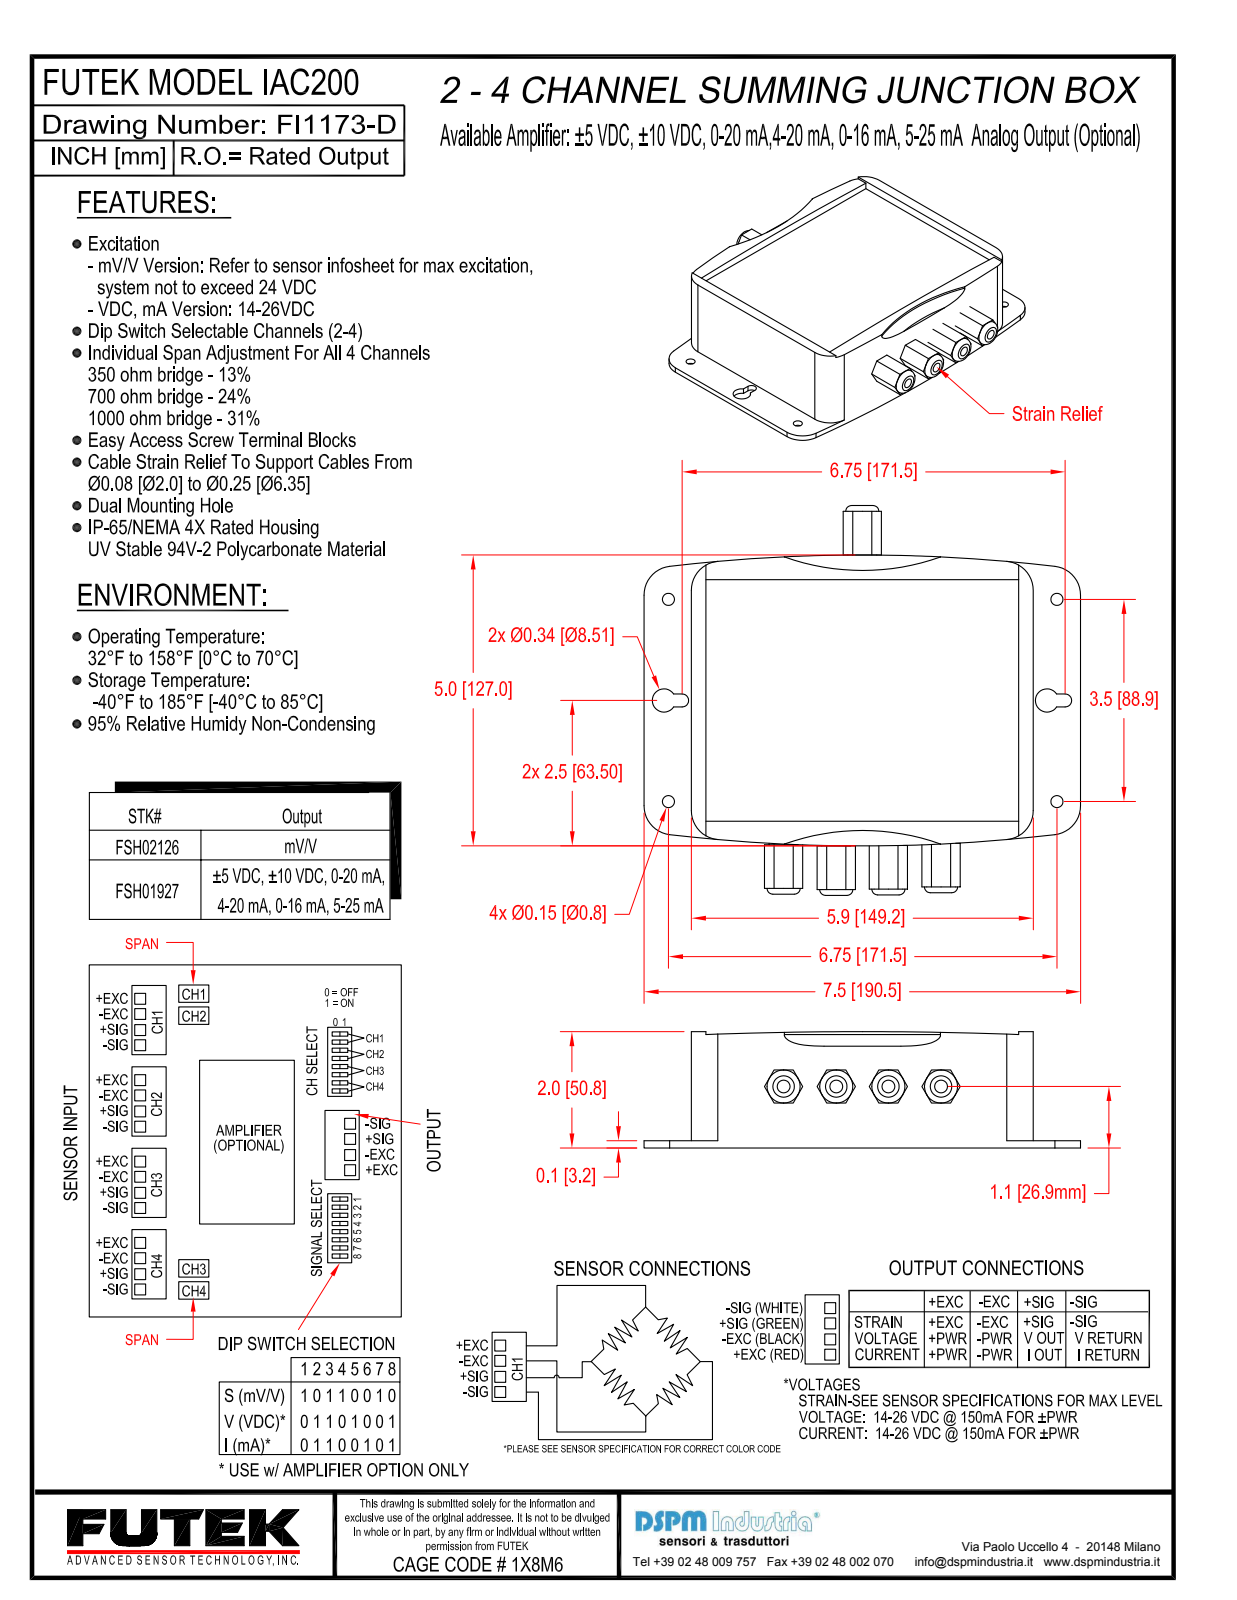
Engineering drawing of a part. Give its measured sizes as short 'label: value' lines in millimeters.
name: FI1173-D
written by: Mechanical Desktop 2009 (CONFIG_CONTROL_DESIGN)
unit: mm
bodies: 6 solids, 172 faces (104 planar, 56 cylindrical, 12 other)
size: 7.5 × 6.7 × 2
volume: 54 mm³; area: 143 mm²
holes: 5× ⌀0.22, 5× ⌀0.5, 4× ⌀0.21, 2× ⌀0.4
rounds: 8× R0.5, 2× R0.11, 2× R3.98, 2× R28.25, 1× R72.62
face distances: 1.79, 5.87, 1.67, 0.57, 1.88, 2, 1.56, 0.78, 1.17, 0.77
hole spacings: 0.9, 0.45, 1.35, 1.74, 1.8, 3.47, 6.67, 6.73
